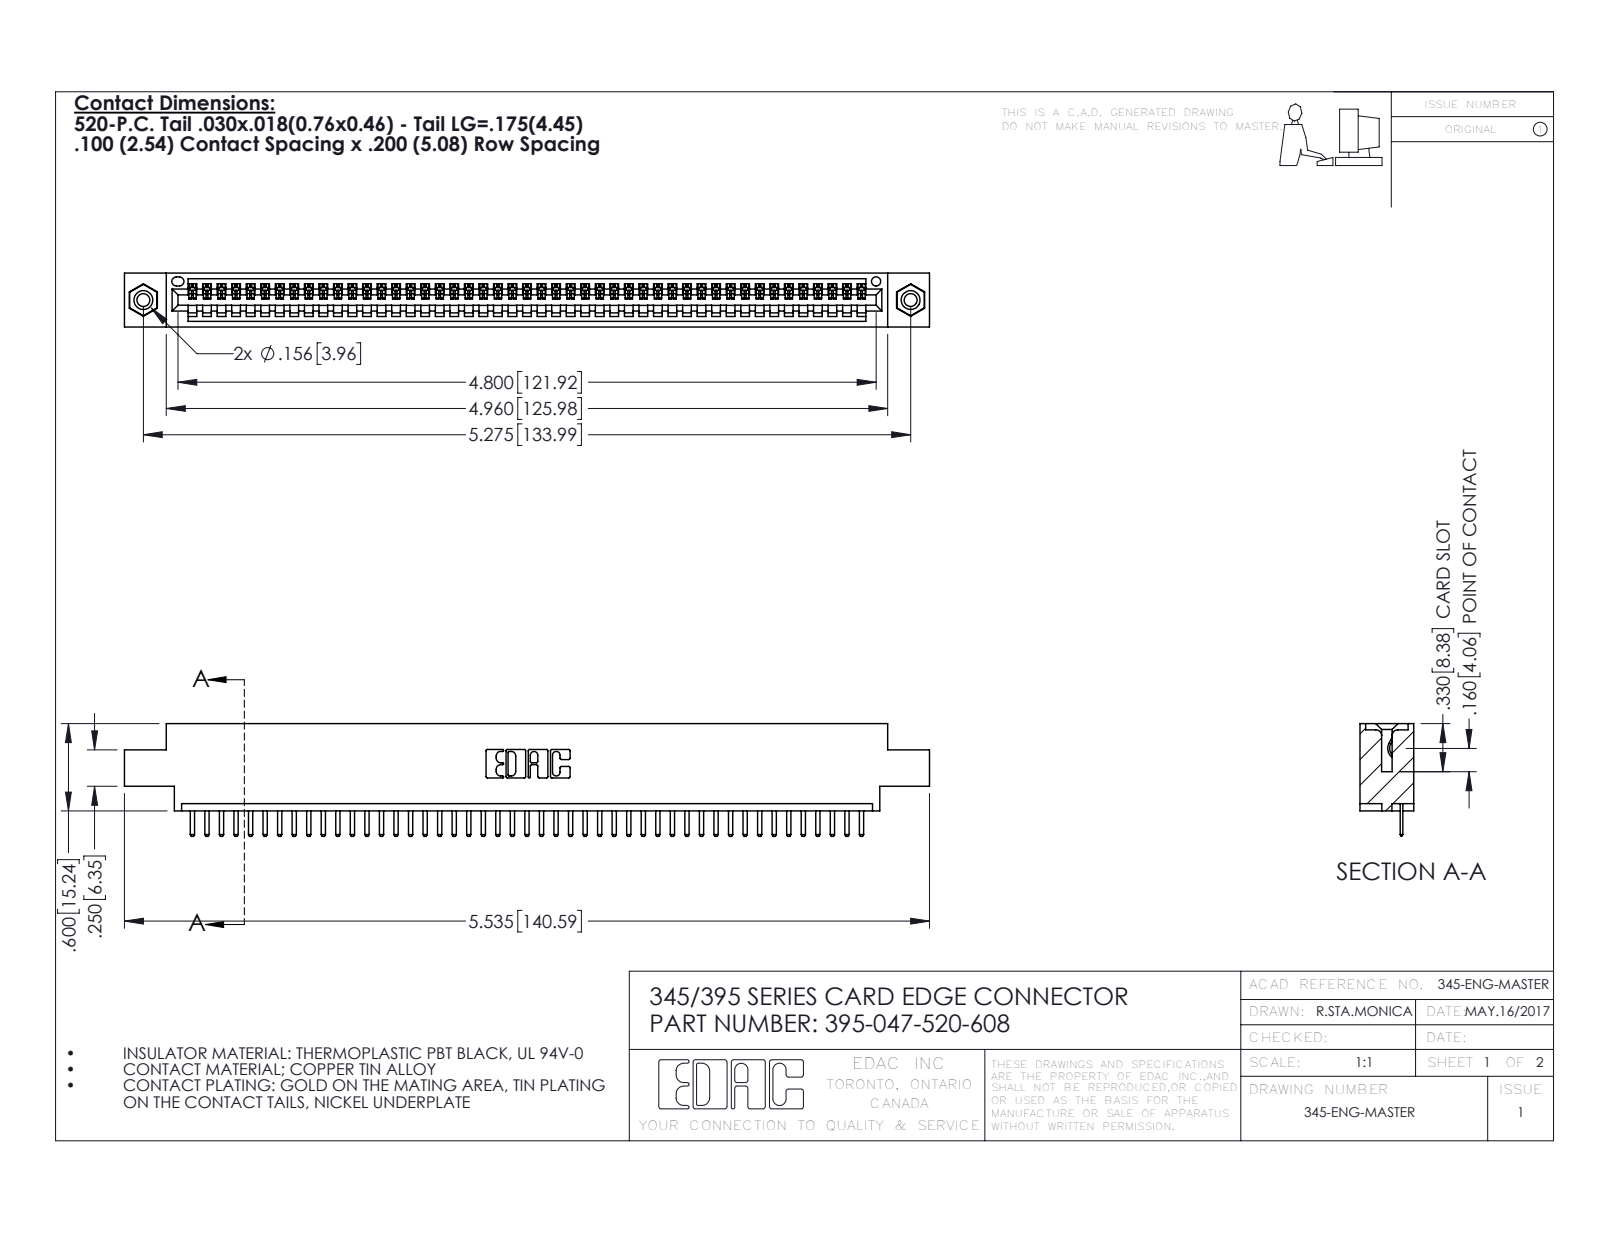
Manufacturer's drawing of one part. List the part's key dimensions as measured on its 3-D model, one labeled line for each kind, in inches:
Part name (STEP PRODUCT): 395-047-520-608; 345-292-001_345-293-120; 345-250-001_345-250-003-102; 345 Part_0.170 Offset - 0.156 Dia-TI
STEP written by: SolidWorks 2016 (CONFIG_CONTROL_DESIGN)
Units: inches
Bodies: 50 solids, 3104 faces (2090 planar, 998 cylindrical, 16 other)
Overall size (bounding box): 5.535 × 0.775 × 0.37
Volume: 0.802 in³ · Surface area: 26.71 in²
Round holes (diameter × count): ⌀0.089 ×2, ⌀0.125 ×2, ⌀0.156 ×2, ⌀0.064 ×1
Round bosses / shafts (diameter × count): ⌀0.155 ×2
Partial cylindrical surfaces — rounded edges, fillets, slot ends (radius × count): R0.01 ×96, R0.006 ×94, R0.01 ×22, R0.007 ×6, R0.031 ×6, R0.026 ×3, R0.031 ×2, R0.04 ×2
Main face-to-face distances: 0.072, 0.298, 0.37, 0.2, 0.098, 0.272, 0.025, 0.225, 0.072, 0.175
Hole centre spacings: 0.27, 5.039, 5.275
